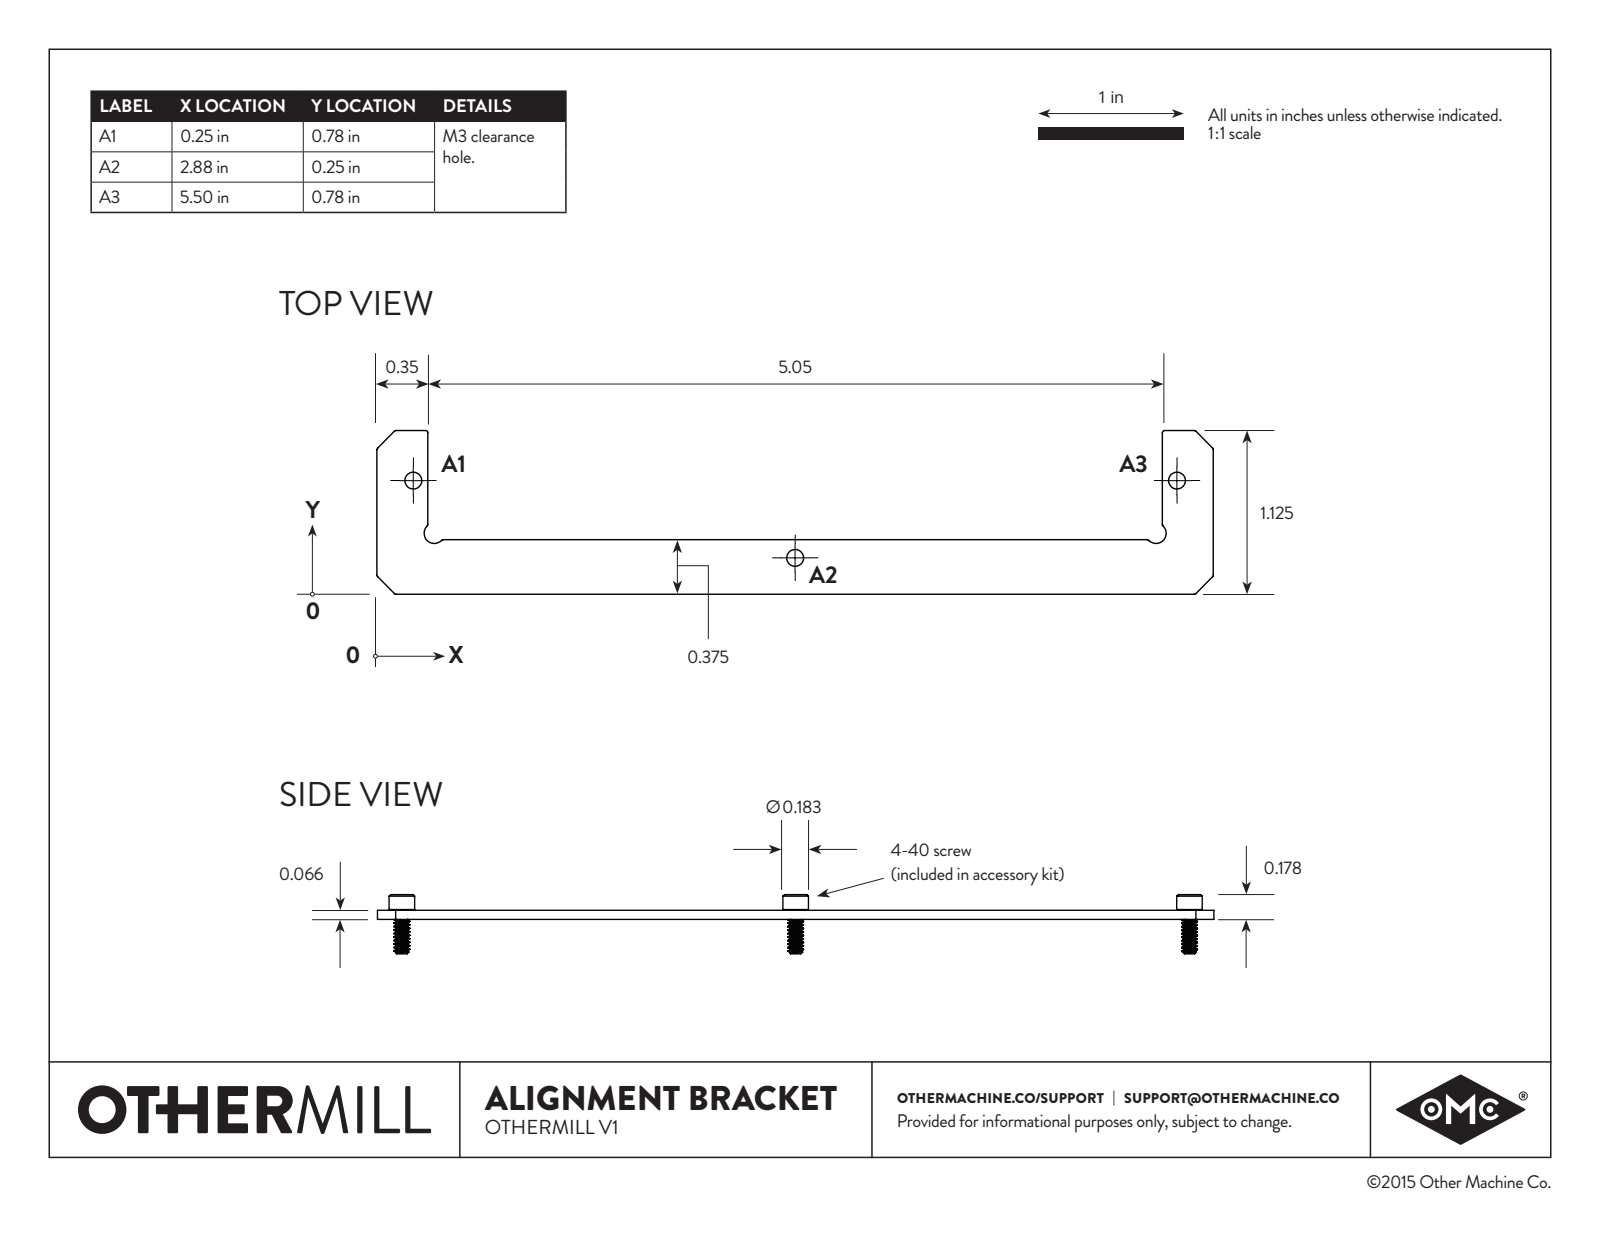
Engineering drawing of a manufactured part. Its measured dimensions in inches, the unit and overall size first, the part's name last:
Units: inches
Overall size (bounding box): 5.75 × 1.125 × 0.06
Round holes (diameter × count): ⌀0.116 ×3
Partial cylindrical surfaces — rounded edges, fillets, slot ends (radius × count): R0.015 ×14, R0.07 ×2
Main face-to-face distances: 0.06, 0.375, 0.35, 5.4, 5.75, 5.05, 1.125, 0.75, 4.684
Hole centre spacings: 2.678, 5.25
Volume: 0.157 in³ · Surface area: 6.187 in²
Bodies: 1 solid, 37 faces (14 planar, 23 cylindrical, 0 other)
Part name (STEP PRODUCT): double sided jig
STEP written by: SolidWorks 2015 (CONFIG_CONTROL_DESIGN)
